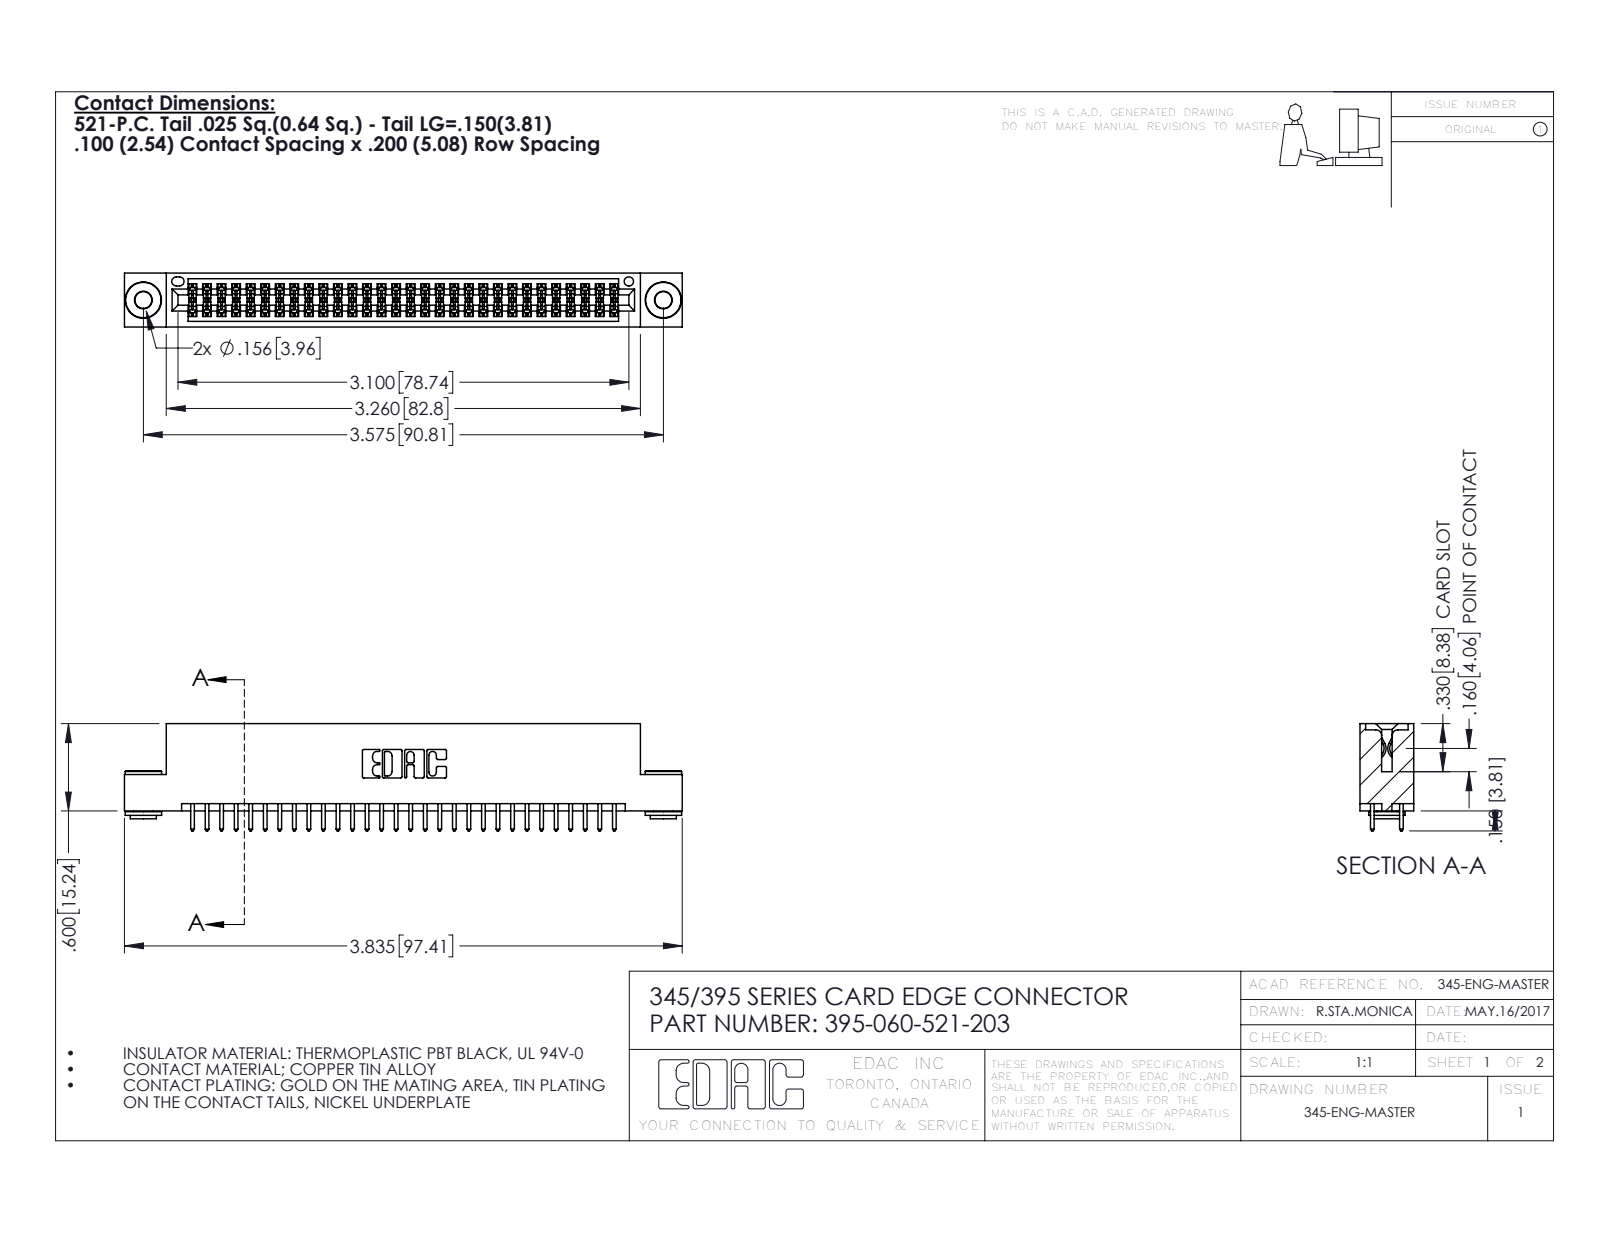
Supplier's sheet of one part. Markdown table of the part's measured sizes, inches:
| quantity | value |
| --- | --- |
| part name | 345 Part_Flush Mounting Lugs - 0.156 Dia-TH; 345-292-001_345-293-121; 345-250-002_345-250-002-102; 395-060-521-203 |
| STEP written by | SolidWorks 2016 (CONFIG_CONTROL_DESIGN) |
| units | inches |
| bodies | 63 solids, 3164 faces (2070 planar, 1086 cylindrical, 8 other) |
| overall size | 3.835 × 0.737 × 0.37 |
| volume | 0.57 in³ |
| surface area | 21.12 in² |
| round holes (diameter × count) | 0.116 × 2, 0.156 × 2, 0.064 × 1 |
| round bosses / shafts (diameter × count) | 0.25 × 2, 0.18 × 2, 0.136 × 2 |
| partial cylindrical surfaces (radius × count) | 0.006 × 90, 0.01 × 60, 0.01 × 22, 0.007 × 6, 0.031 × 6, 0.026 × 3, 0.014 × 2, 0.019 × 2 |
| main face-to-face distances | 0.072, 0.298, 0.2, 0.37, 0.025, 0.098, 0.272, 0.225, 0.175, 0.149 |
| hole center spacings | 0.27, 3.34, 3.575 |
